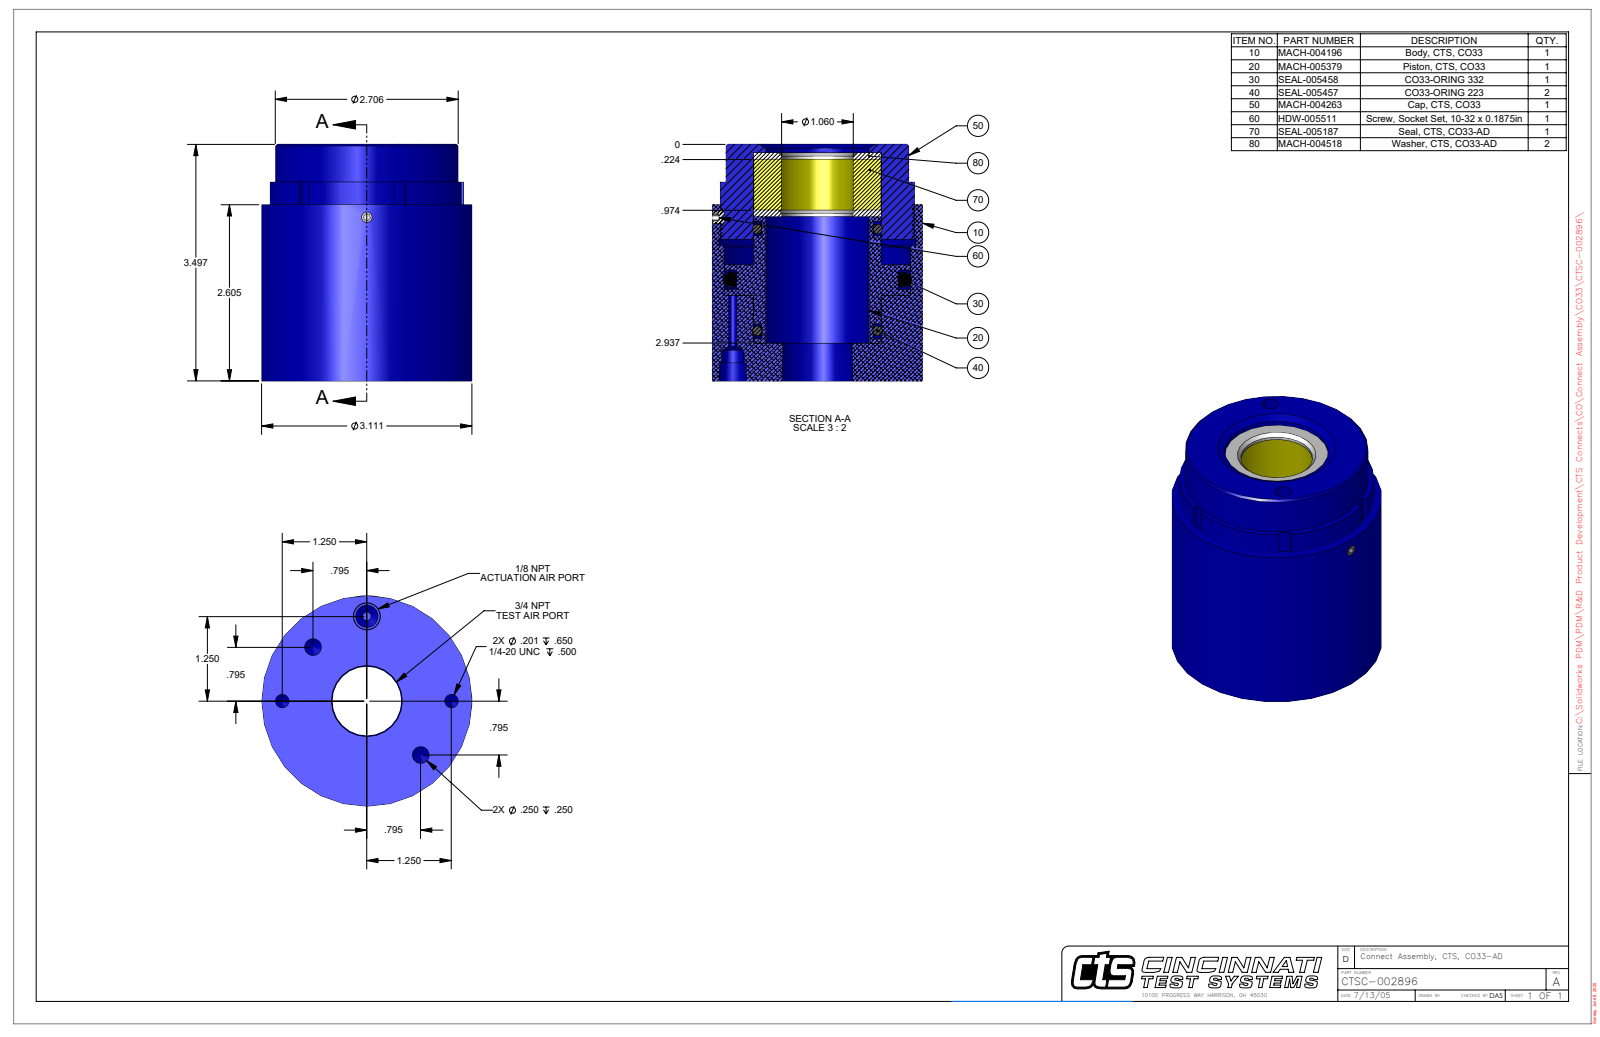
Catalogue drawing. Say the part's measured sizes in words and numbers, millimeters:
The part is named "CTSC-002896". Its 3-D file was written by "SolidWorks 2023 (AUTOMOTIVE_DESIGN)". It is 1 solid with 122 faces: 49 planar, 53 cylindrical and 20 other. Overall it measures 88.8 by 79 by 79 millimeters. Its volume is 328 100 cubic millimeters and its surface area 42 820 square millimeters. Round holes: 4 of diameter 6.4, 2 of diameter 5.1, 1 of diameter 2.4, 1 of diameter 3.2, 1 of diameter 4, 1 of diameter 8.4, 1 of diameter 26.9, 1 of diameter 27, 1 of diameter 38.8, 1 of diameter 38.8, 1 of diameter 48.1. Round bosses or shafts: 1 of diameter 79, 1 of diameter 73, 1 of diameter 68.7, 1 of diameter 47.9. Partial cylindrical surfaces (rounded edges, fillets, slot ends): 1 of radius 35.7, 1 of radius 39.2. The main face-to-face distances are 88.8, 14.2, 74.6, 66.2, 22.7, 51.9, 61.7, 47.5, 4.5, 27.1. The hole center spacings are 28.6, 23.3, 31.8, 55.8, 2.4, 25.6, 44.9, 54.7.
